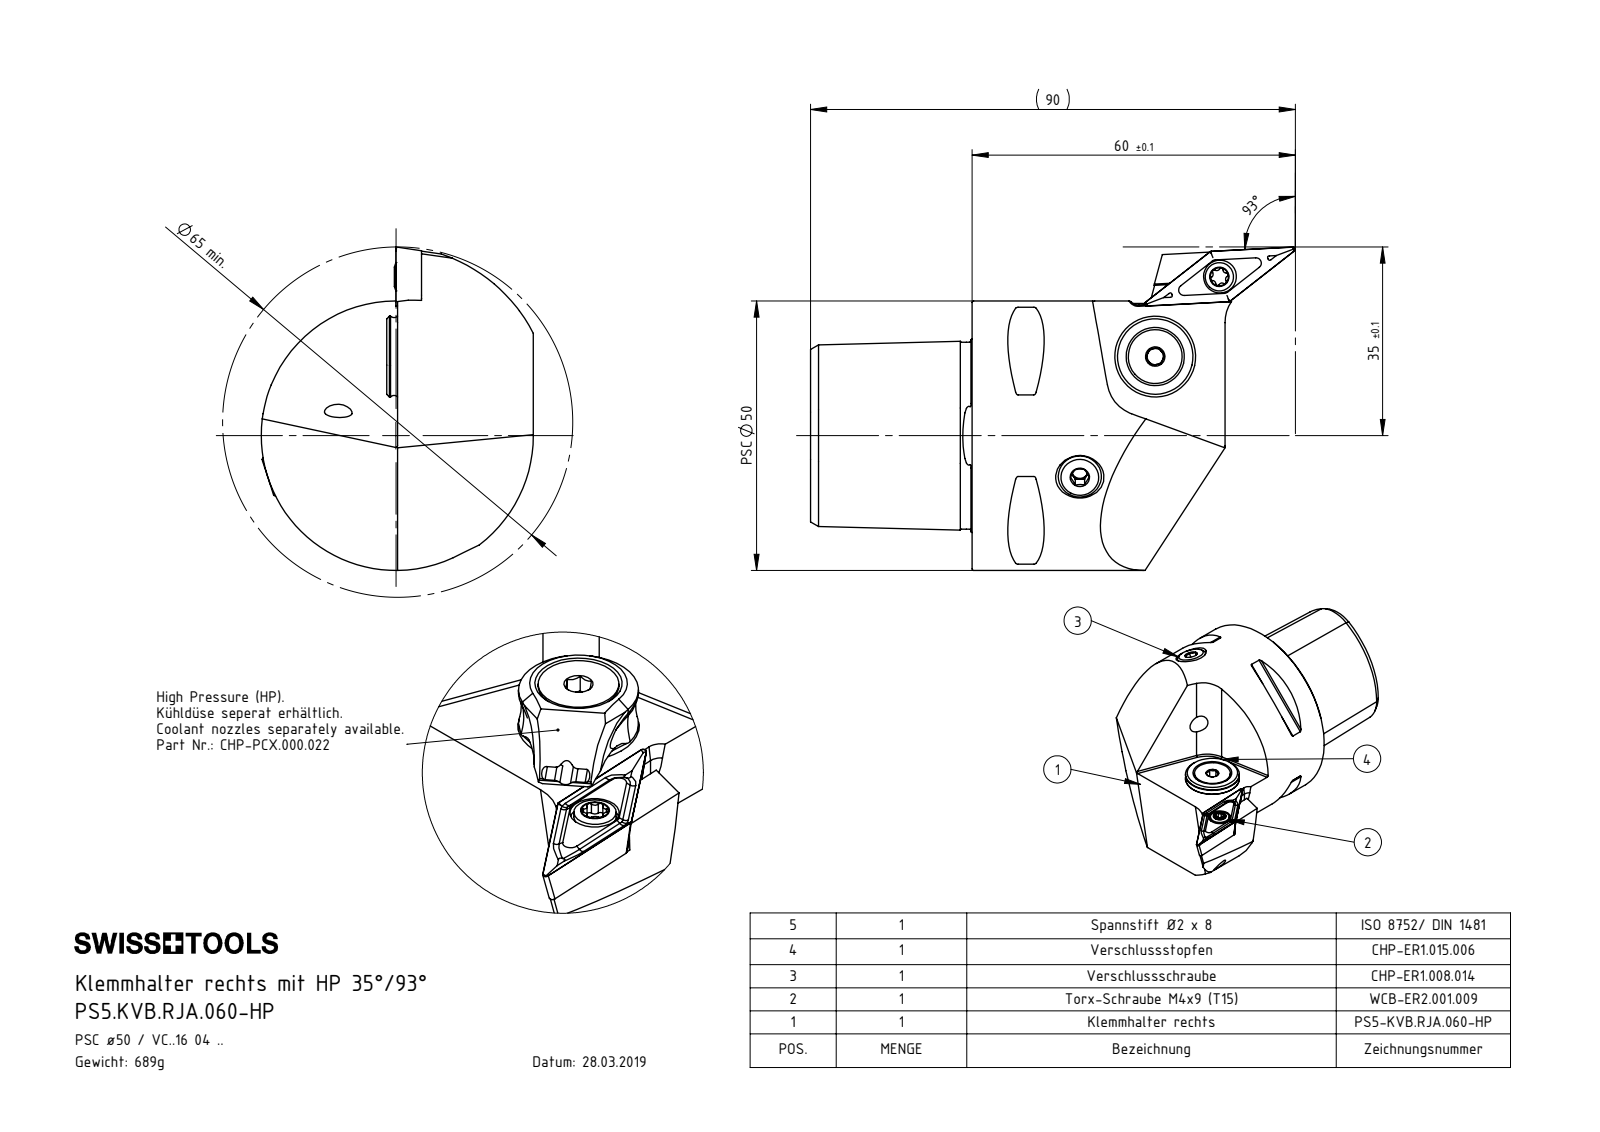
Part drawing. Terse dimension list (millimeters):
name: PS5.KVB.RJA.060-HP; WCB-ER2.001.009_A; CHP-ER1.015.006_A; VCMT160404 (+6 more)
written by: SolidWorks 2017 (AUTOMOTIVE_DESIGN)
unit: mm
bodies: 8 solids, 278 faces (94 planar, 62 cylindrical, 122 other)
size: 90 × 60 × 50.5
volume: 87 666 mm³; area: 21 386 mm²
holes: 2× ⌀4.2, 2× ⌀5, 2× ⌀6.1, 1× ⌀1.2, 1× ⌀2, 1× ⌀2.5, 1× ⌀3, 1× ⌀3.3, 1× ⌀4, 1× ⌀4.4, 1× ⌀5.2, 1× ⌀7
bosses: 1× ⌀50, 1× ⌀15, 1× ⌀13.4, 1× ⌀10, 1× ⌀8, 1× ⌀5.5, 1× ⌀5.25, 1× ⌀5
rounds: 8× R0.5, 6× R0.34, 6× R0.59, 2× R0.4, 2× R7, 1× R1.75, 1× R4, 1× R25.5
face distances: 30, 4.5, 4.46, 20.7, 20.74, 25.2, 19.18, 44.4, 10, 20
hole spacings: 4.5, 15.07, 15.17, 18.99, 19.09, 26, 26.45, 29.89
